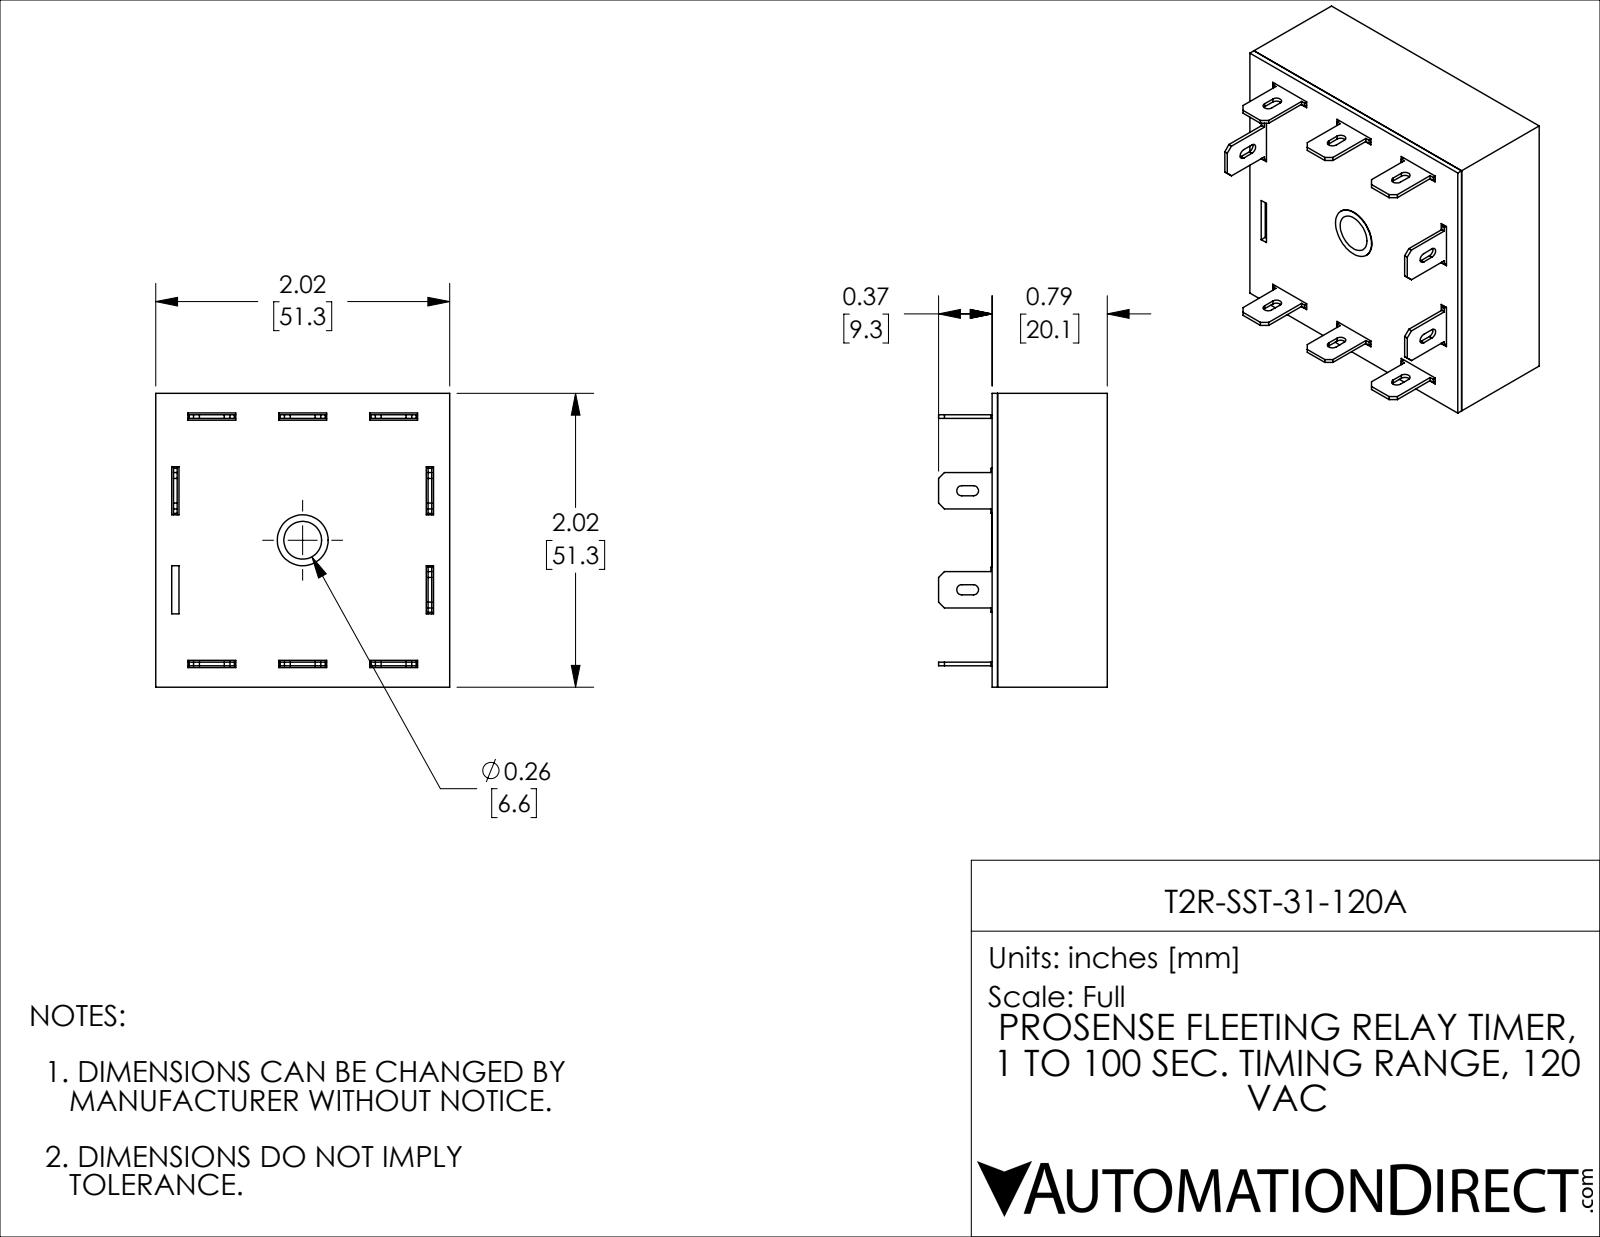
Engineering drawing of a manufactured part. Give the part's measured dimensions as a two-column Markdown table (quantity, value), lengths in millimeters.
| quantity | value |
| --- | --- |
| part name | T2R-SST-31-120A |
| STEP written by | SolidWorks 2021 (CONFIG_CONTROL_DESIGN) |
| units | millimeters |
| bodies | 11 solids, 280 faces (256 planar, 22 cylindrical, 2 other) |
| overall size | 51.31 × 51.31 × 29.46 |
| volume | 11 178 mm³ |
| surface area | 23 301 mm² |
| round holes (diameter × count) | 8.89 × 1 |
| partial cylindrical surfaces (radius × count) | 0.89 × 10 |
| main face-to-face distances | 1.14, 50.16, 19.15, 20.12, 0.97, 18.01, 18.98, 51.3, 3.74, 47.56 |
